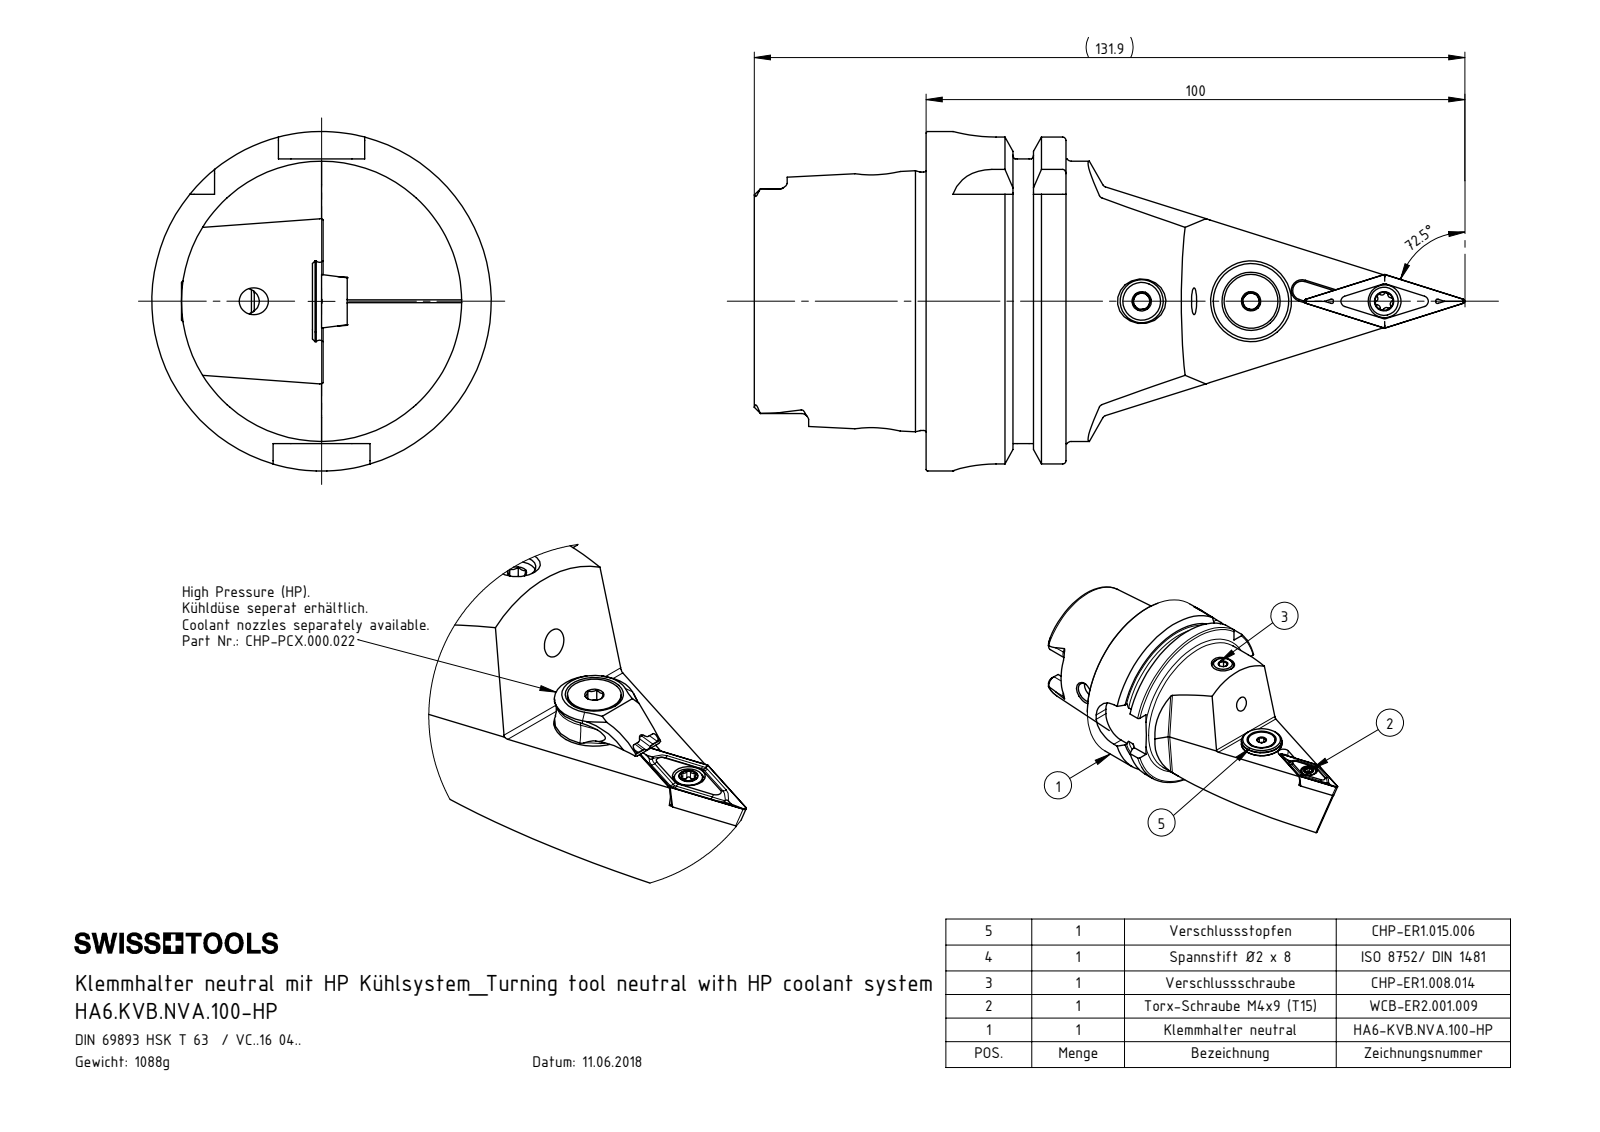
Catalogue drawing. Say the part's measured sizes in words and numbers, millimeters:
The part is named "CHP-ER1.015.006_A; WCB-ER2.001.009_A; ISO 8752 2x8; VCMT160404 (+6 more)". Its 3-D file was written by "SolidWorks 2017 (AUTOMOTIVE_DESIGN)". It is 8 solids with 313 faces: 122 planar, 77 cylindrical and 114 other. Overall it measures 131.9 by 63 by 63 millimeters. Its volume is 138 526 cubic millimeters and its surface area 32 861 square millimeters. Round holes: 3 of diameter 5, 2 of diameter 4.2, 1 of diameter 1.2, 1 of diameter 2, 1 of diameter 2.5, 1 of diameter 3, 1 of diameter 3.3, 1 of diameter 4.4, 1 of diameter 5.2, 1 of diameter 6.1, 1 of diameter 7, 1 of diameter 7.5. Round bosses or shafts: 1 of diameter 63, 1 of diameter 54.95, 1 of diameter 52, 1 of diameter 47.94, 1 of diameter 15, 1 of diameter 13.4, 1 of diameter 10, 1 of diameter 8. Partial cylindrical surfaces (rounded edges, fillets, slot ends): 6 of radius 0.34, 6 of radius 0.59, 6 of radius 1.4, 5 of radius 0.8, 4 of radius 8, 2 of radius 2.82, 2 of radius 2.88, 1 of radius 1.75. The main face-to-face distances are 25.95, 16, 9.95, 31.9, 41.85, 57.85, 52.8, 21.8, 11.85, 4.5. The hole center spacings are 4.5, 21.48, 20.3, 21.38, 21.58, 23.89, 23.97, 24.69.
